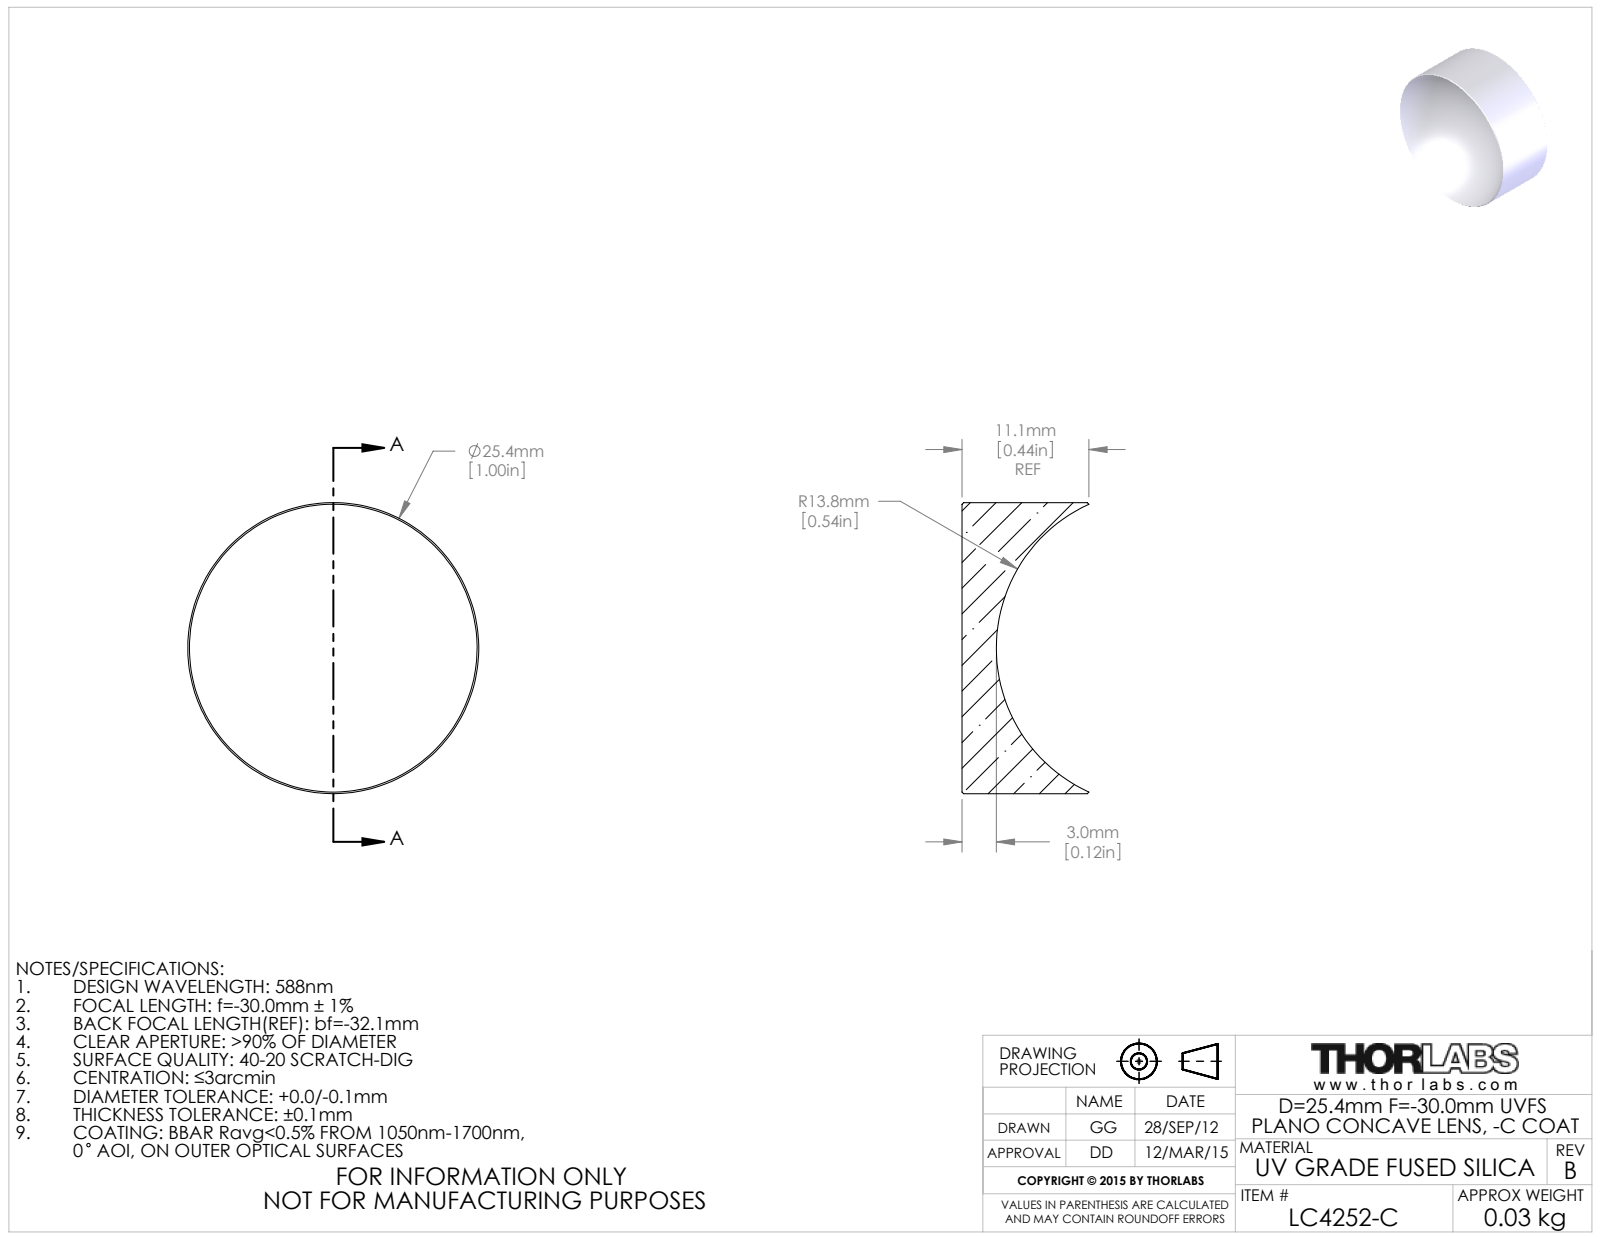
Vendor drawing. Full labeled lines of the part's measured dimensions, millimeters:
Part name (STEP PRODUCT): 25025-E0W
STEP written by: SolidWorks 2011 (CONFIG_CONTROL_DESIGN)
Units: millimetres
Bodies: 1 solid, 9 faces (1 planar, 2 cylindrical, 6 other)
Overall size (bounding box): 25.4 × 25.4 × 11.08
Volume: 3 335 mm³ · Surface area: 2 089 mm²
Round bosses / shafts (diameter × count): ⌀25.4 ×1
